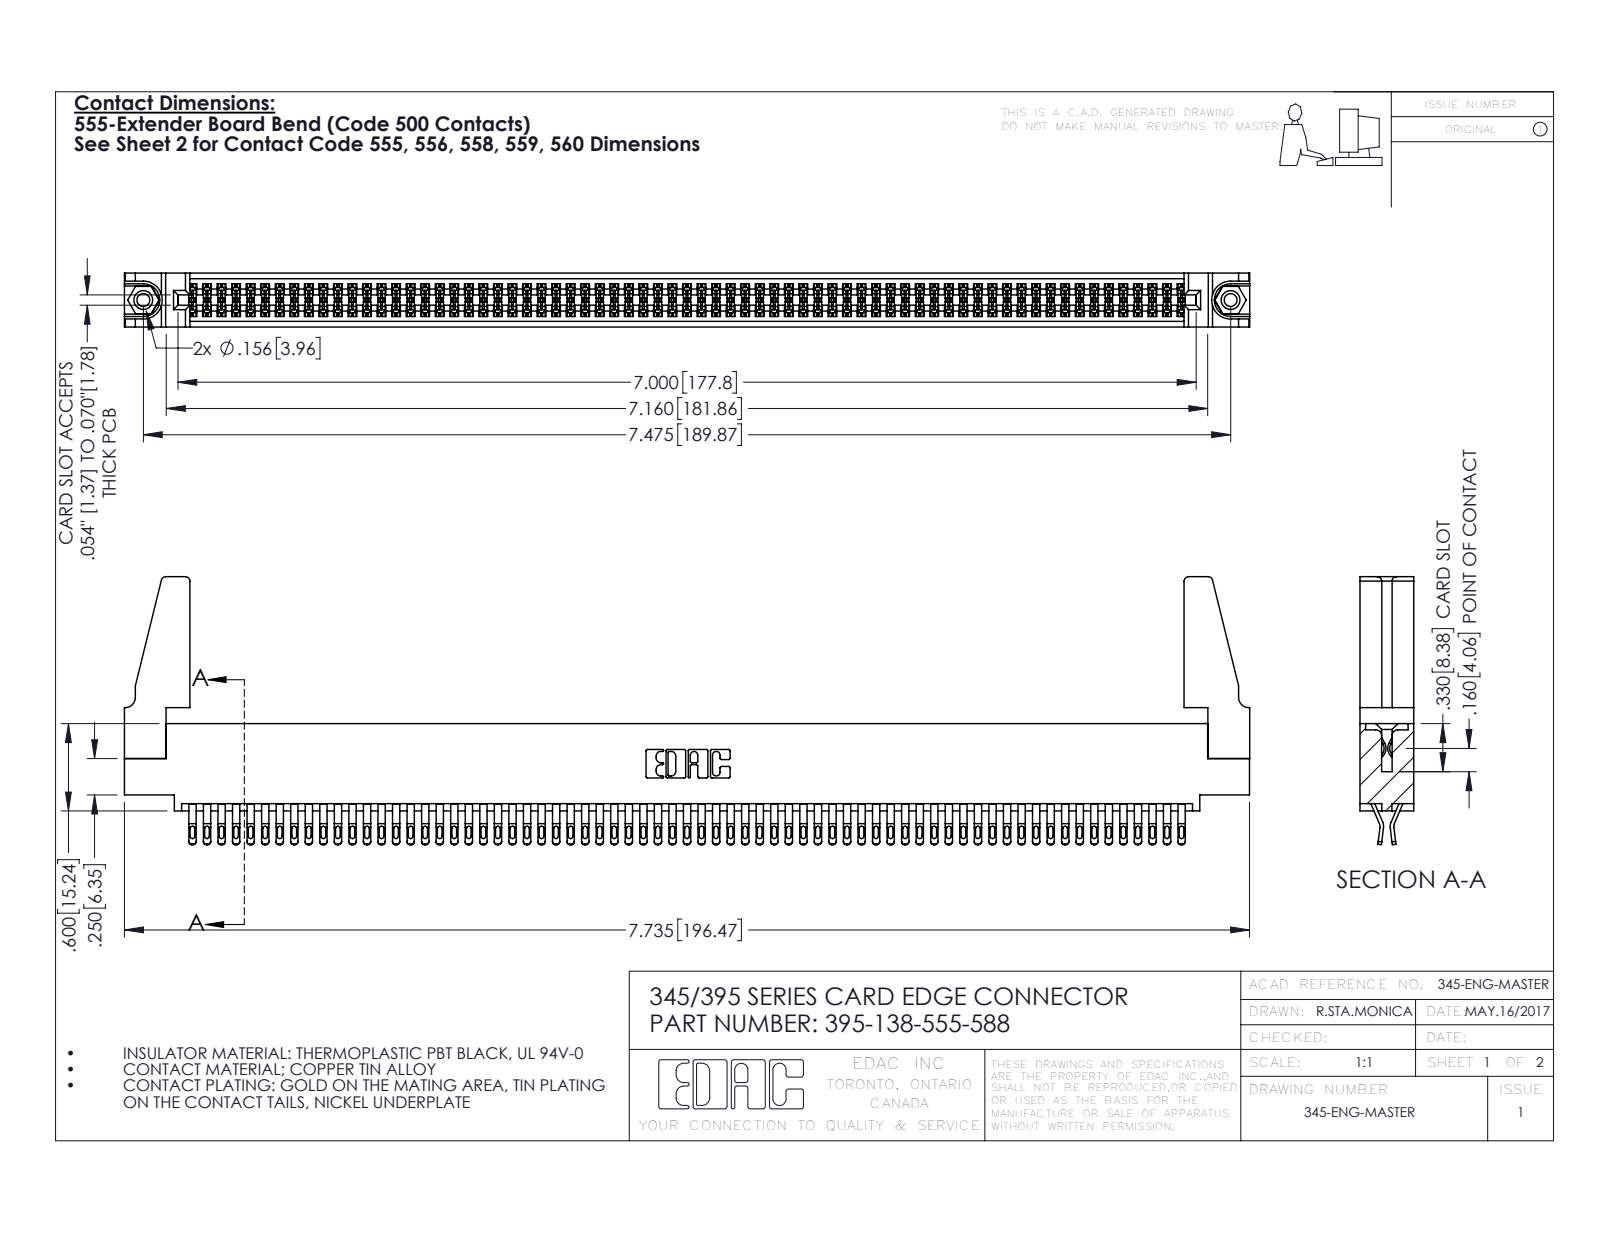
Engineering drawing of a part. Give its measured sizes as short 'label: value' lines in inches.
name: 345-292-001_555 Tail; 345-220-078_345-220-088; 395-138-555-588; 345-250-001_345-250-001-102 (+1 more)
written by: SolidWorks 2016 (CONFIG_CONTROL_DESIGN)
unit: in
bodies: 143 solids, 7982 faces (4434 planar, 3532 cylindrical, 16 other)
size: 7.736 × 1.842 × 0.37
volume: 1.399 in³; area: 53.01 in²
holes: 2× ⌀0.089, 2× ⌀0.125, 2× ⌀0.156, 1× ⌀0.064
bosses: 2× ⌀0.155
rounds: 345× R0.016, 276× R0.02, 207× R0.006, 22× R0.01, 8× R0.03, 6× R0.007, 6× R0.031, 3× R0.026
face distances: 0.072, 0.298, 0.37, 0.025, 0.098, 0.272, 0.2, 0.225, 0.175, 0.149
hole spacings: 0.27, 7.239, 7.475
